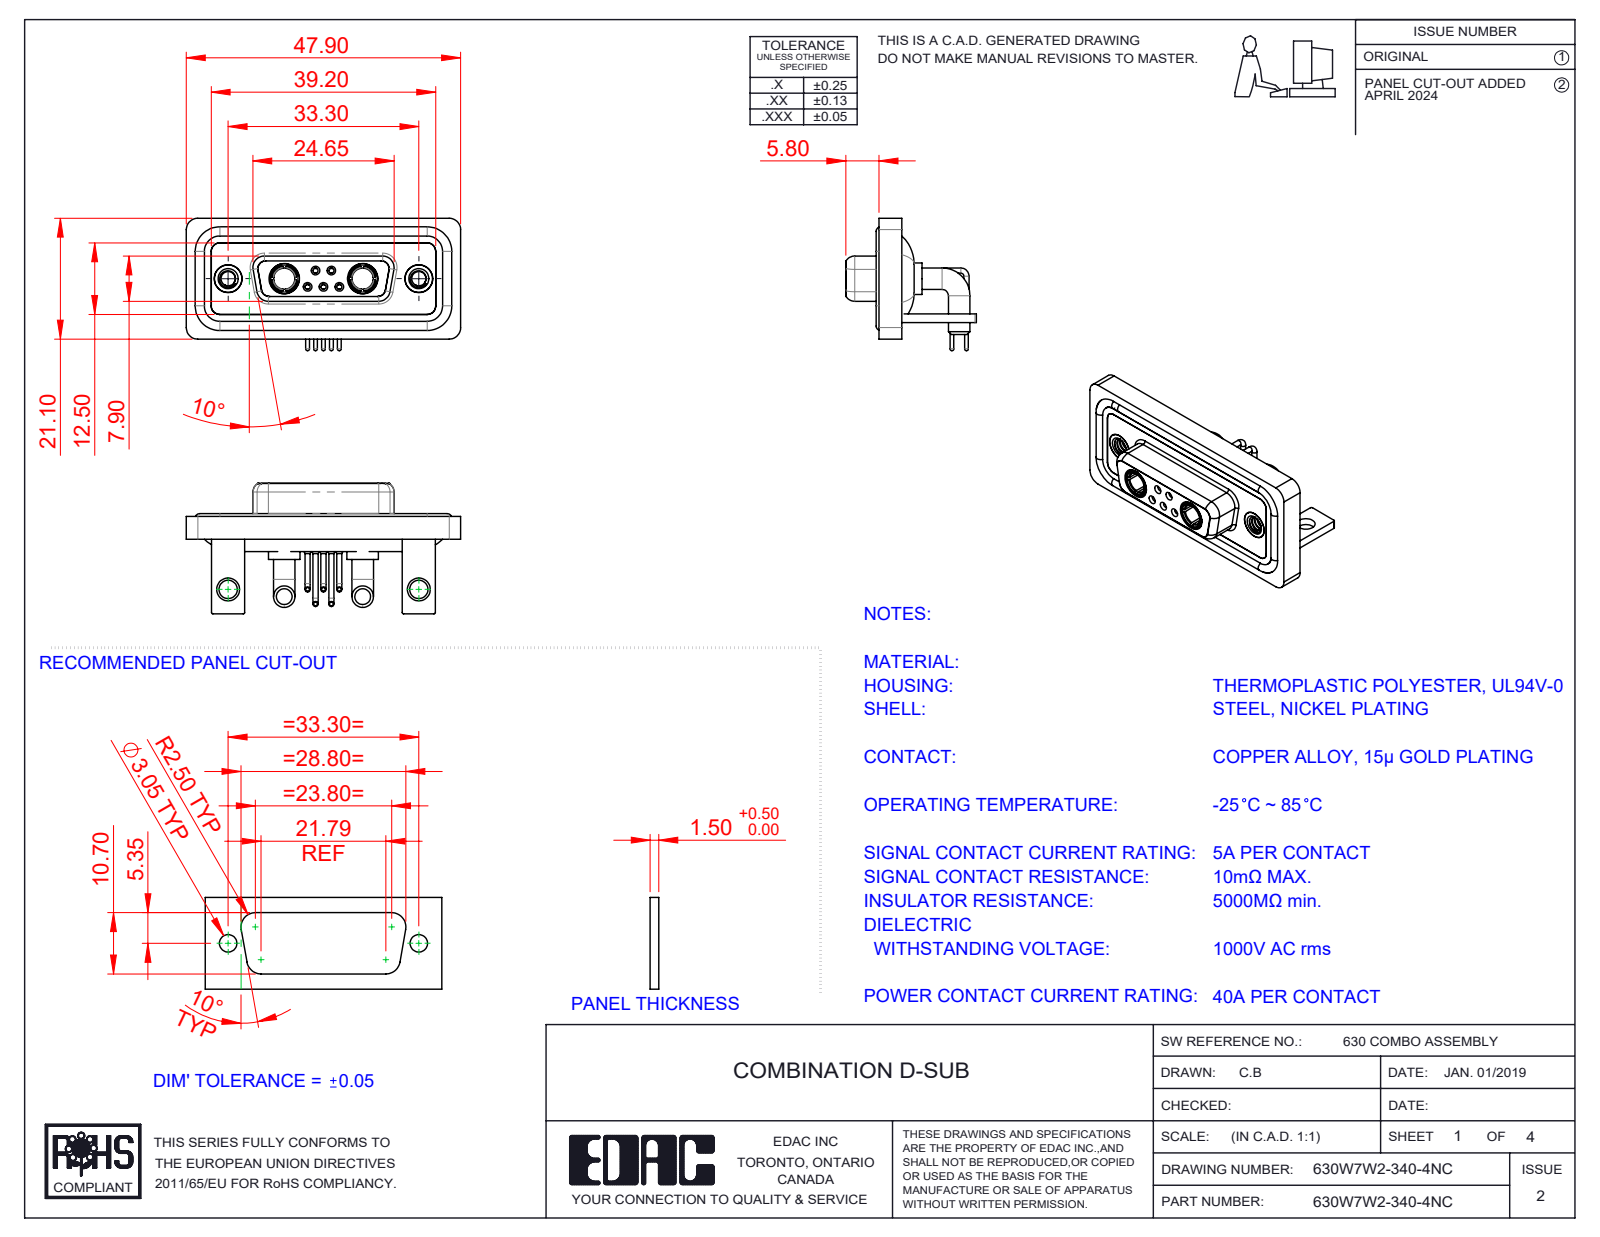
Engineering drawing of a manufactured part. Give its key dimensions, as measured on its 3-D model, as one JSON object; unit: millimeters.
{"part_name": "630Combo Housing_7W2; 630Combo Contact Row 1_50 Contacts; Power Socket_40A RA; 630Combo Shell Rear_15 Contacts (+6 more)", "step_written_by": "SolidWorks 2023 (CONFIG_CONTROL_DESIGN)", "units": "millimeters", "bodies": {"solids": 18, "faces": 849, "planar": 258, "cylindrical": 375, "other": 216}, "overall_size": [47.9, 23.12, 22.8], "volume_mm3": 6701, "surface_area_mm2": 11032, "round_holes": [[0.9, 5], [1.1, 5], [1.5, 5], [2, 5], [4.85, 4], [1.6, 3], [1.7, 2], [2.5, 2], [3.2, 2], [3.7, 2], [4, 2], [4.05, 2]], "round_bosses_or_shafts": [[1.6, 6], [0.9, 5], [0.65, 5], [3.75, 4], [5.5, 2], [5.2, 2], [4.96, 2], [4.95, 2]], "partial_cylinders_radius": [[2, 21], [1.5, 18], [0.25, 16], [1.35, 12], [1.6, 8], [0.5, 5], [0.6, 4], [0.65, 4]], "face_to_face_distances": [0.4, 2.9, 1.5, 1.8, 3.7, 1.1, 4.1, 1.6, 2.5, 1.4], "hole_center_spacings": [3.16, 2.77, 9.8, 23.5, 33.3, 4.31, 4.33, 5.03]}
